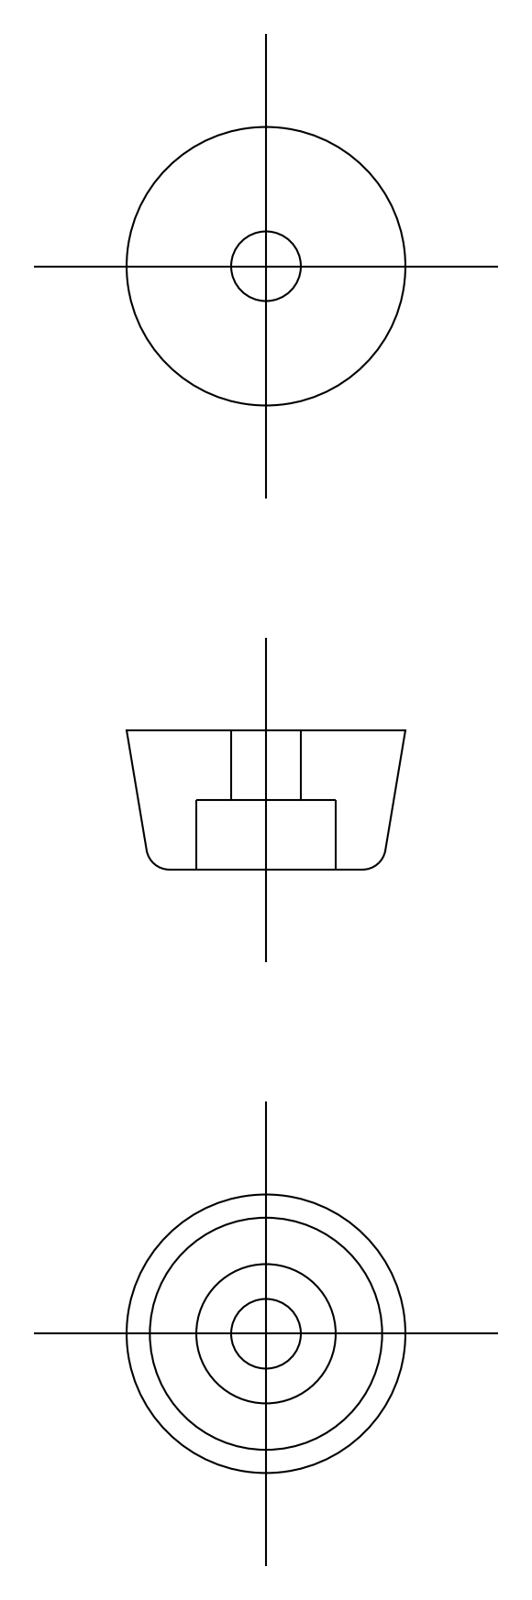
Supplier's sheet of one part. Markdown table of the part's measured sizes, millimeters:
| quantity | value |
| --- | --- |
| part name | washer; rubber foot; CK_11_1045_36 |
| STEP written by | CADfix (AUTOMOTIVE_DESIGN) |
| units | millimeters |
| bodies | 2 solids, 23 faces (0 planar, 0 cylindrical, 23 other) |
| overall size | 12 × 12 × 6 |
| volume | 463 mm³ |
| surface area | 619 mm² |
